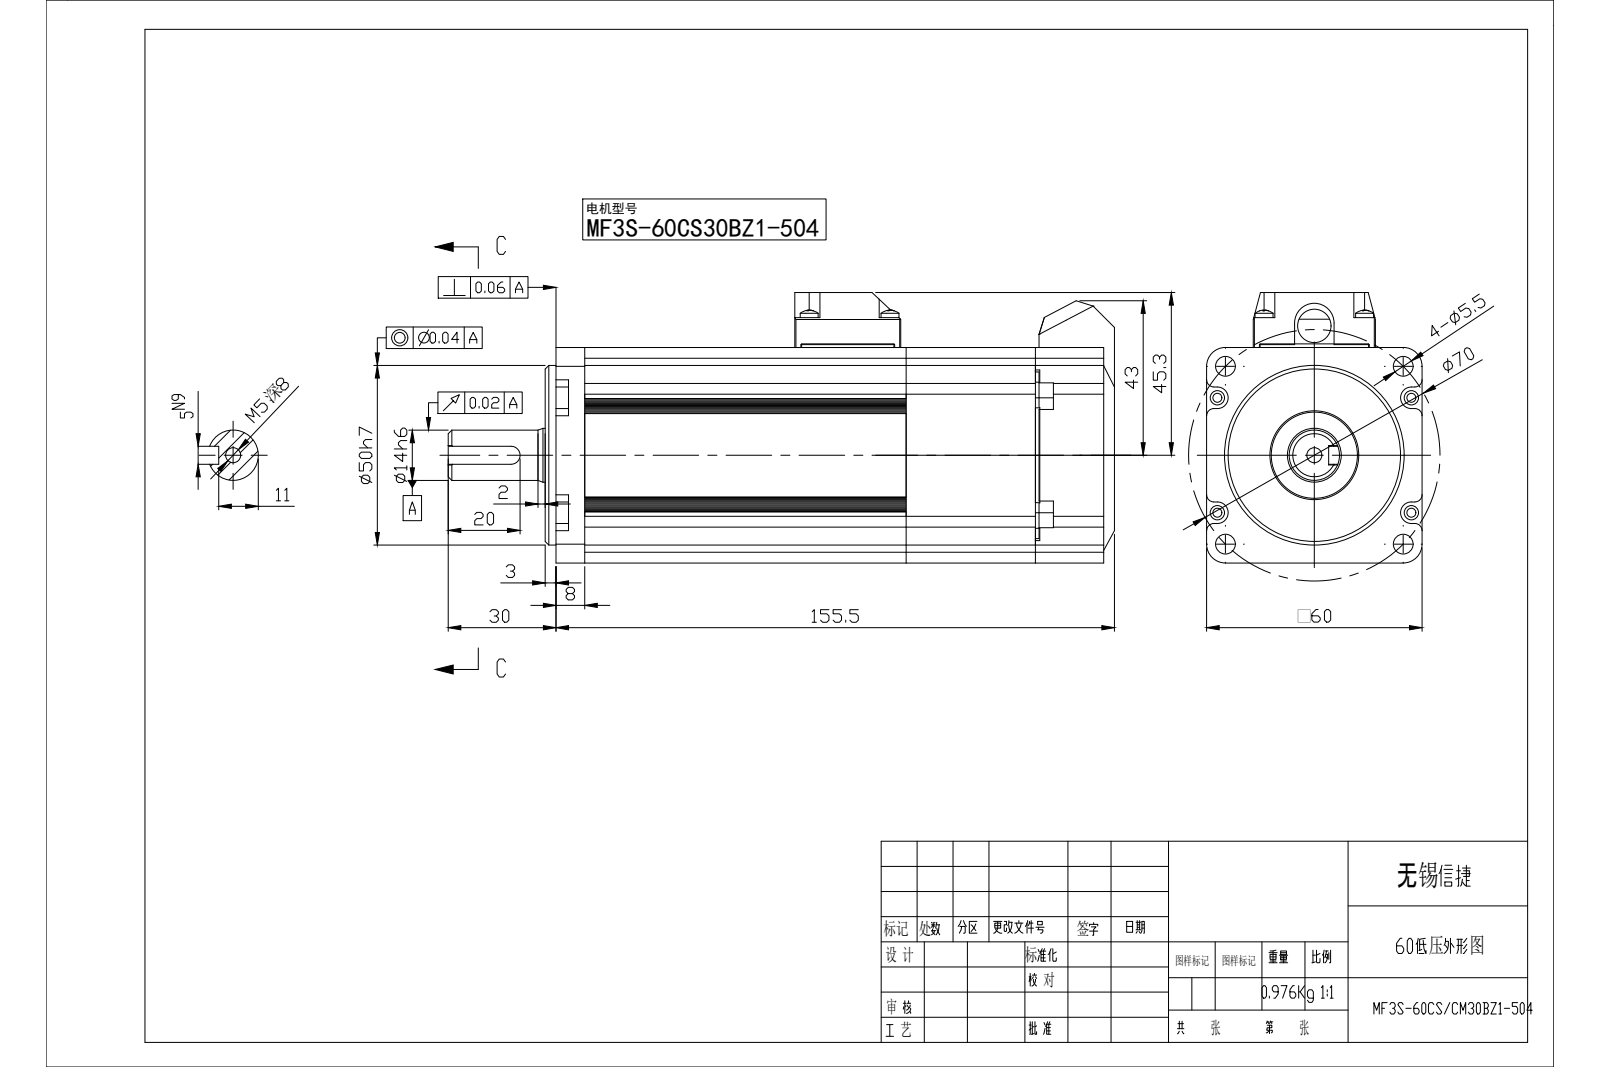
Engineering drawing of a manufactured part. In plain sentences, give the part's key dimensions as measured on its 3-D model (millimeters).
Its 3-D file was written by "SolidWorks 2016 (CONFIG_CONTROL_DESIGN)". It is 0 solids with 461 faces: 181 planar, 257 cylindrical and 23 other. Overall it measures 185.5 by 75.3 by 60 millimeters. Round holes: 8 of diameter 3.5, 6 of diameter 3, 5 of diameter 5.5, 4 of diameter 4, 1 of diameter 4.2, 1 of diameter 6.3, 1 of diameter 9.3. Round bosses or shafts: 4 of diameter 5, 1 of diameter 50, 1 of diameter 24, 1 of diameter 15, 1 of diameter 14, 1 of diameter 5.6. Partial cylindrical surfaces (rounded edges, fillets, slot ends): 90 of radius 0.15, 16 of radius 3, 8 of radius 2, 4 of radius 0.2, 4 of radius 0.3, 4 of radius 2.8, 4 of radius 3.25, 4 of radius 5. The main face-to-face distances are 60, 3, 10, 50, 155.5, 11, 22, 133.5, 158.5, 136.5. The hole center spacings are 8.84, 9.03, 14.87, 30.53, 31.38, 32, 35, 40.77.
